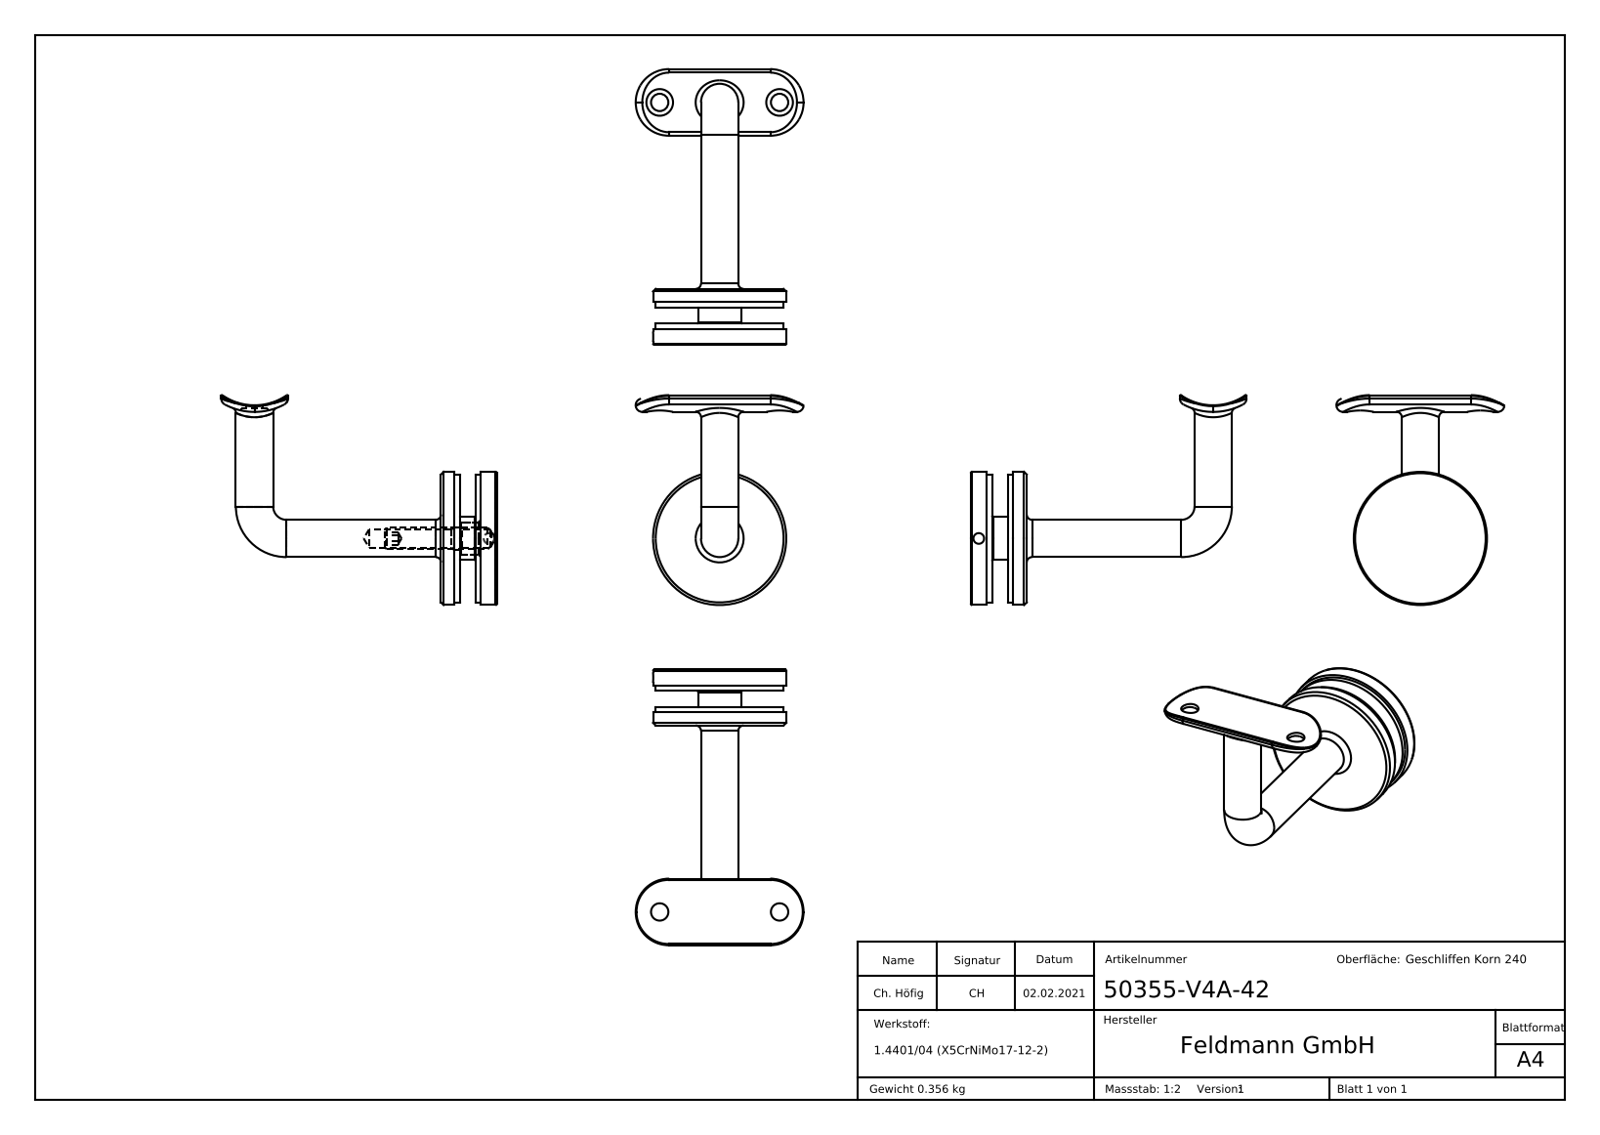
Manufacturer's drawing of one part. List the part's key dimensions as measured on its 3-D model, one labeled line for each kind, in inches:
Part name (STEP PRODUCT): 50355-V4A-XX Teil1_50355-V4A-42 Teil1; 50355-V4A-42; 50355-V4A-XX Teil3; 50355-V4A-XX Teil2 (+7 more)
STEP written by: SolidWorks 2018 (CONFIG_CONTROL_DESIGN)
Units: inches
Bodies: 5 solids, 420 faces (209 planar, 46 cylindrical, 165 other)
Overall size (bounding box): 5.098 × 3.102 × 2.481
Volume: 3.103 in³ · Surface area: 43.32 in²
Round holes (diameter × count): ⌀0.256 ×2, ⌀0.394 ×2, ⌀0.157 ×1, ⌀0.268 ×1, ⌀0.335 ×1, ⌀0.472 ×1
Round bosses / shafts (diameter × count): ⌀0.551 ×2, ⌀1.969 ×1, ⌀1.89 ×1, ⌀0.63 ×1, ⌀0.315 ×1
Partial cylindrical surfaces — rounded edges, fillets, slot ends (radius × count): R0.012 ×2, R0.098 ×2, R0.492 ×2, R0.835 ×1, R0.933 ×1
Main face-to-face distances: 0.315, 0.394, 0.236, 0.079, 0.63, 0.551, 0.197, 0.827, 0.591, 0.512
Hole centre spacings: 1.772
